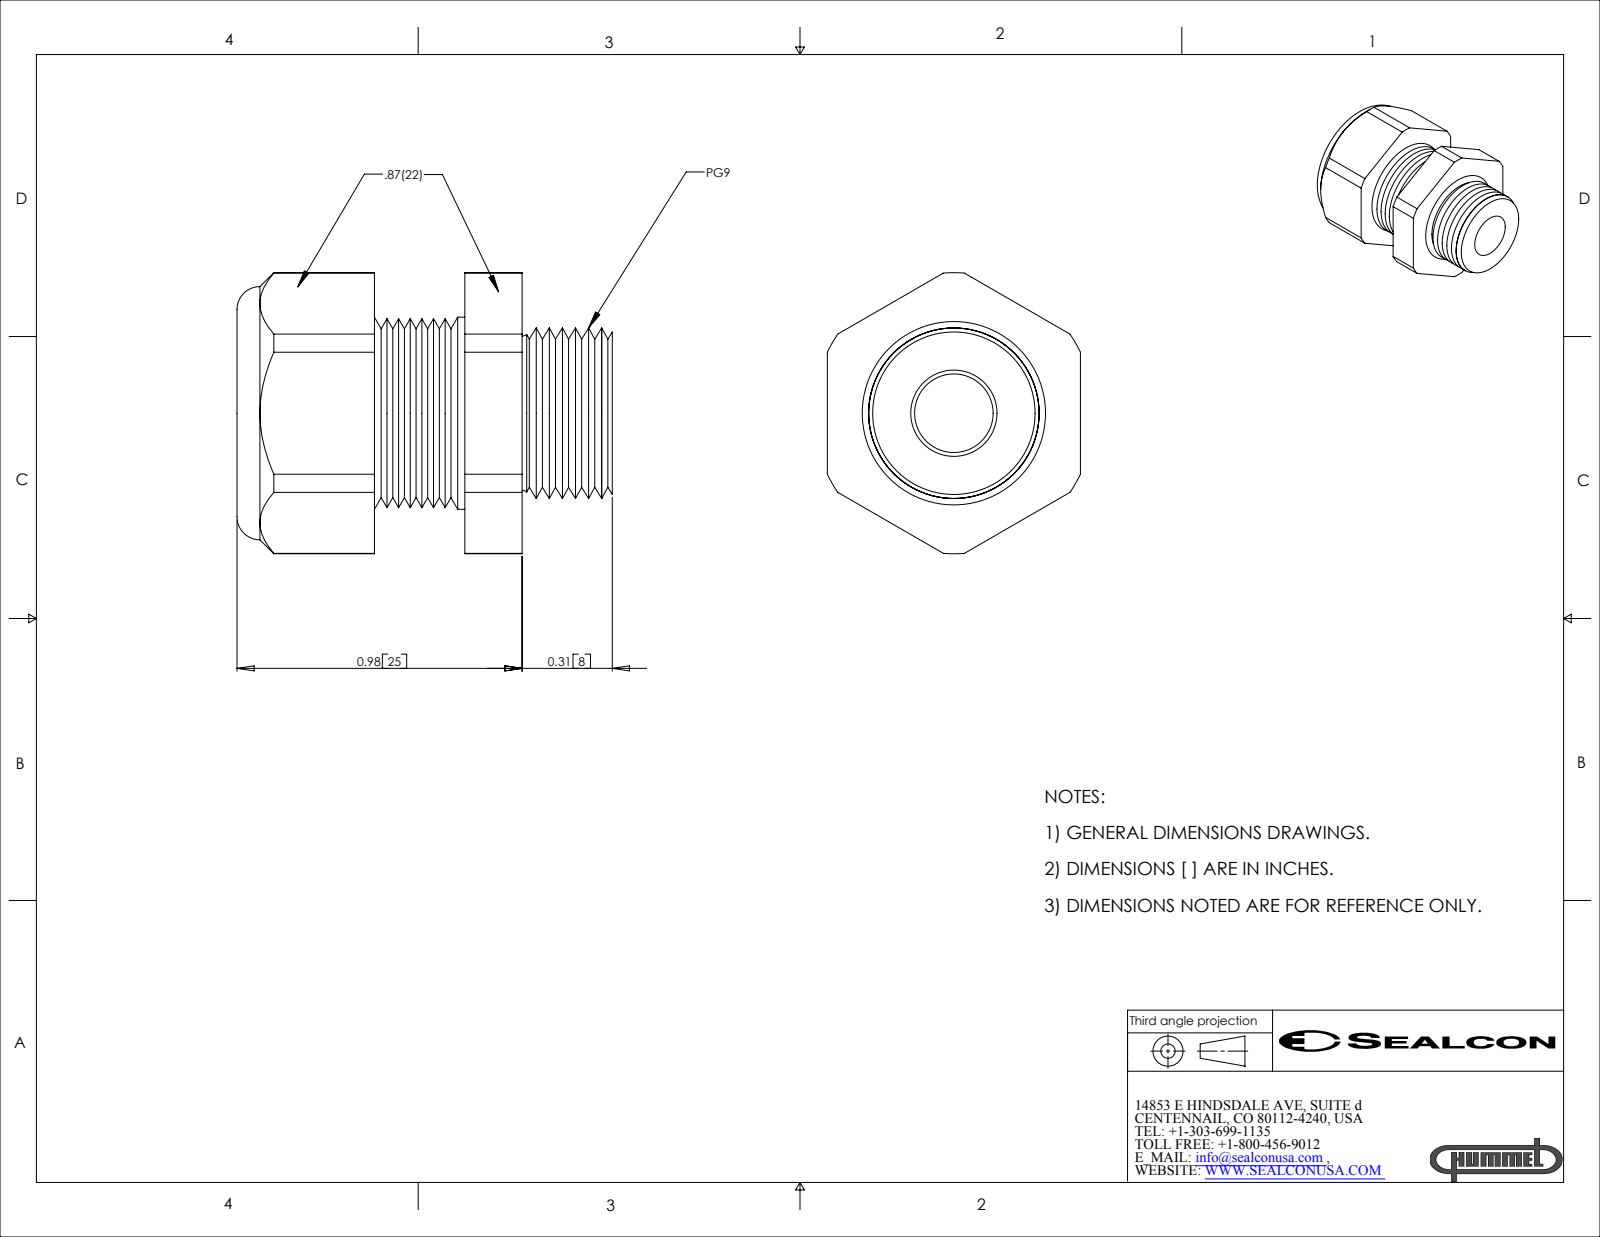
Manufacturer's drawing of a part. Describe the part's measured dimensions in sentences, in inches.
The part is named "CD09GR-GY". Its 3-D file was written by "SolidWorks 2007 (CONFIG_CONTROL_DESIGN)". It is 2 solids with 116 faces: 20 planar, 22 cylindrical and 74 other. Overall it measures 1.29 by 0.966 by 0.87 inches. Its volume is 0.508 cubic inches and its surface area 9.137 square inches. Round holes: 1 of diameter 0.27, 1 of diameter 0.6. Round bosses or shafts: 1 of diameter 0.66. Partial cylindrical surfaces (rounded edges, fillets, slot ends): 1 of radius 0.483. The main face-to-face distances are 0.87, 0.508, 0.311, 0.197, 0.442, 0.753, 0.95, 1.26, 0.818, 0.507.
